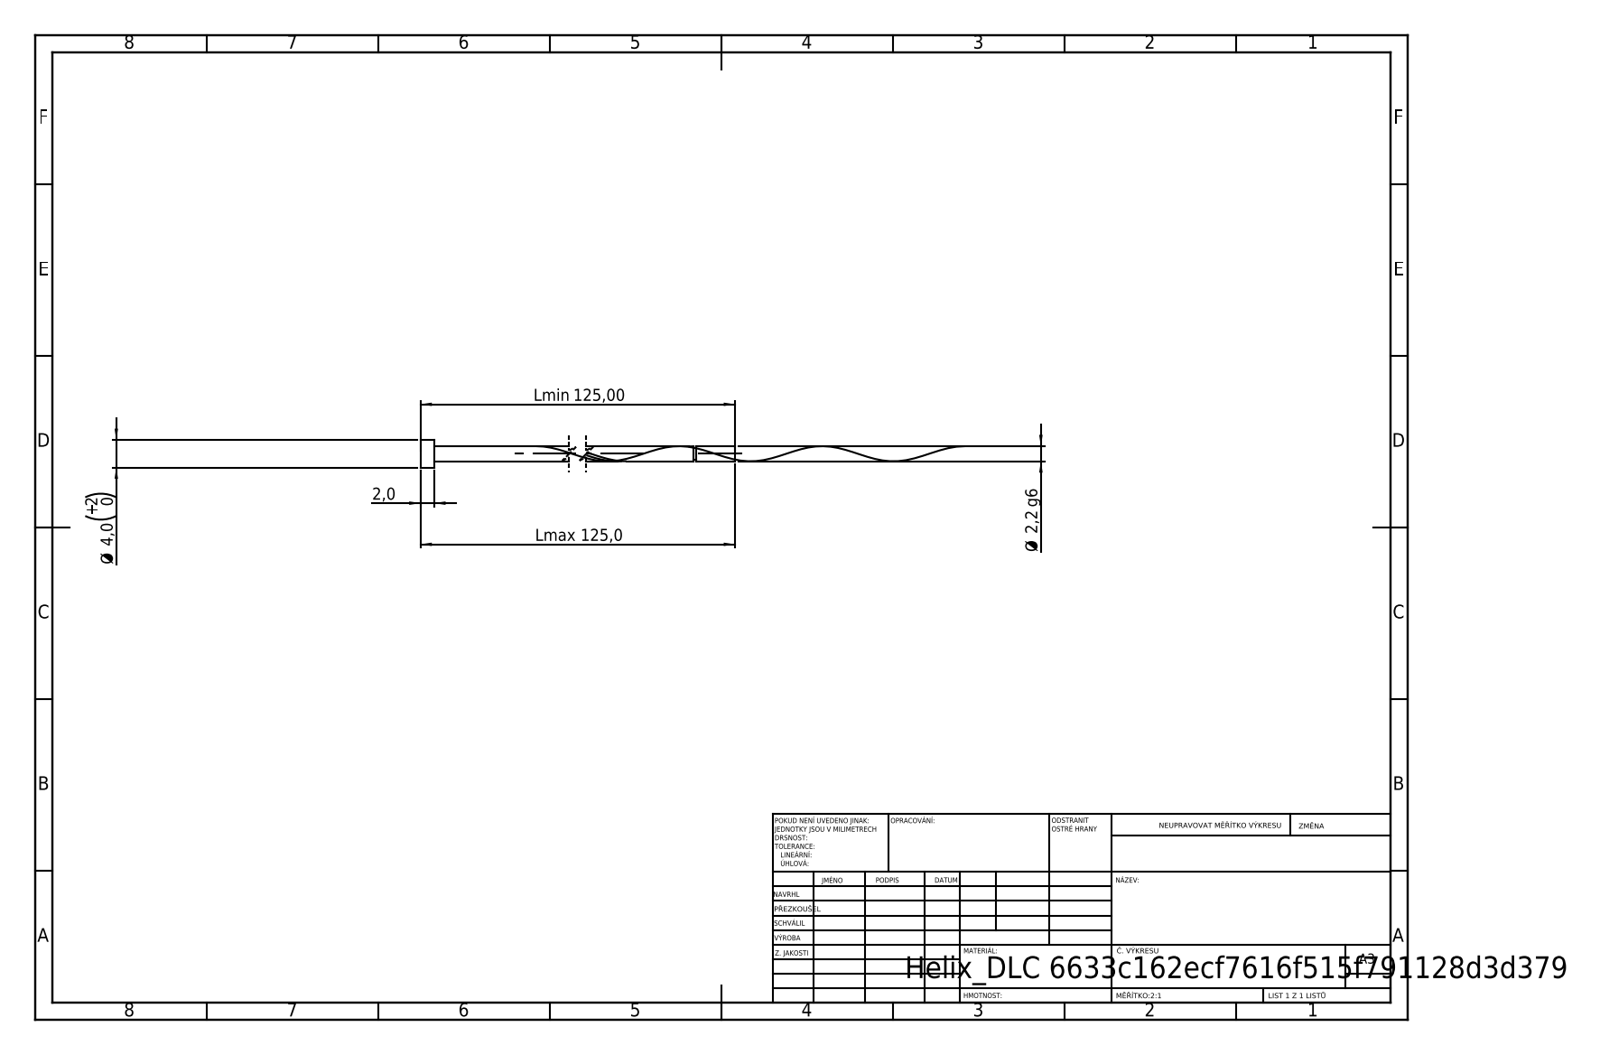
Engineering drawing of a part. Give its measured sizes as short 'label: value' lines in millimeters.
written by: SolidWorks 2019 (CONFIG_CONTROL_DESIGN)
unit: mm
bodies: 1 solid, 16 faces (6 planar, 9 cylindrical, 1 other)
size: 125 × 4 × 4
volume: 593 mm³; area: 1 205 mm²
bosses: 1× ⌀4, 1× ⌀2.2, 1× ⌀1.76
face distances: 2, 125, 123, 119.38, 117.38, 5.62, 118.94, 116.94, 0.44, 6.06
